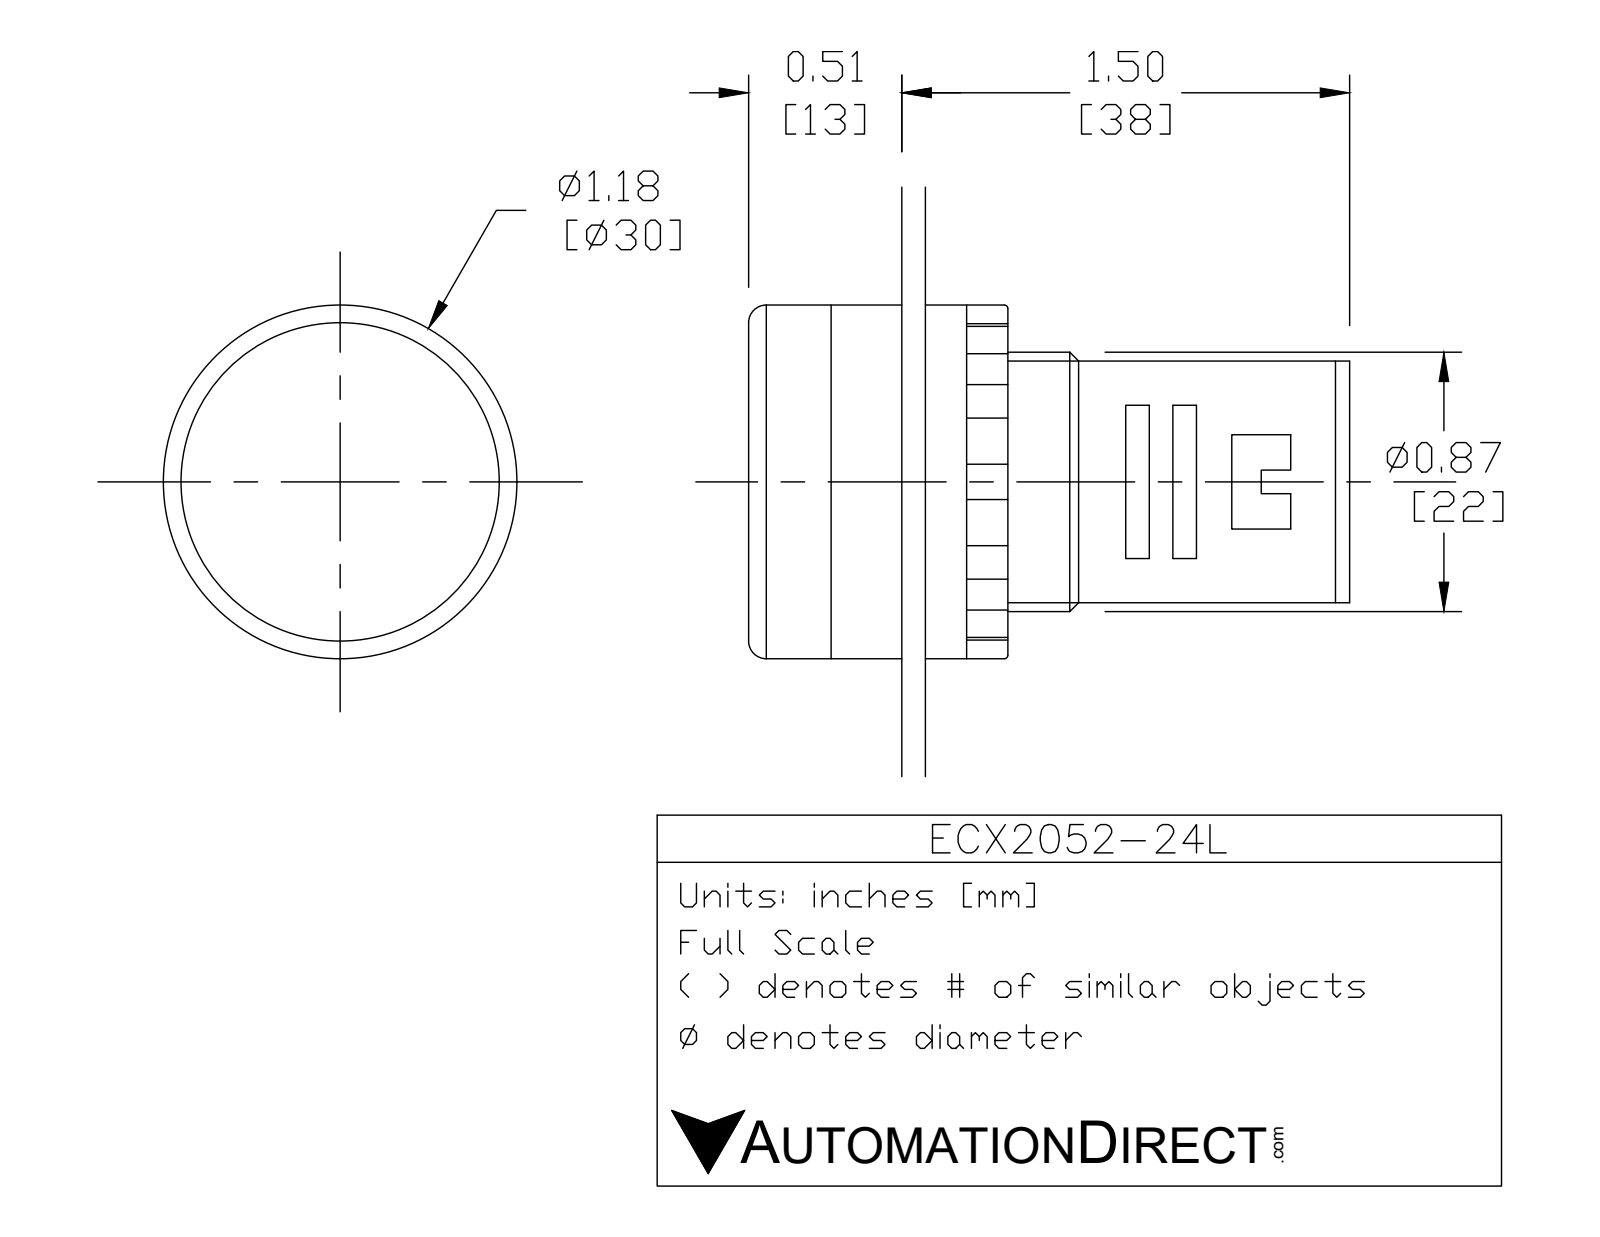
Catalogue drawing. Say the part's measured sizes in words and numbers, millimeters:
The part is named "ECX2052-24L". Its 3-D file was written by "SolidWorks 2017 (AUTOMOTIVE_DESIGN)". It is 6 solids with 123 faces: 63 planar, 39 cylindrical and 21 other. Overall it measures 51 by 30 by 30 millimeters. Its volume is 22 483 cubic millimeters and its surface area 9 831 square millimeters. Round holes: 2 of diameter 5.5, 1 of diameter 22.5. Round bosses or shafts: 2 of diameter 4, 1 of diameter 30, 1 of diameter 29, 1 of diameter 26.5, 1 of diameter 22, 1 of diameter 20. Partial cylindrical surfaces (rounded edges, fillets, slot ends): 12 of radius 1. The main face-to-face distances are 6, 19, 13, 7, 2, 25, 4, 12, 17, 15. The hole center spacings are 4.62, 9.24.
